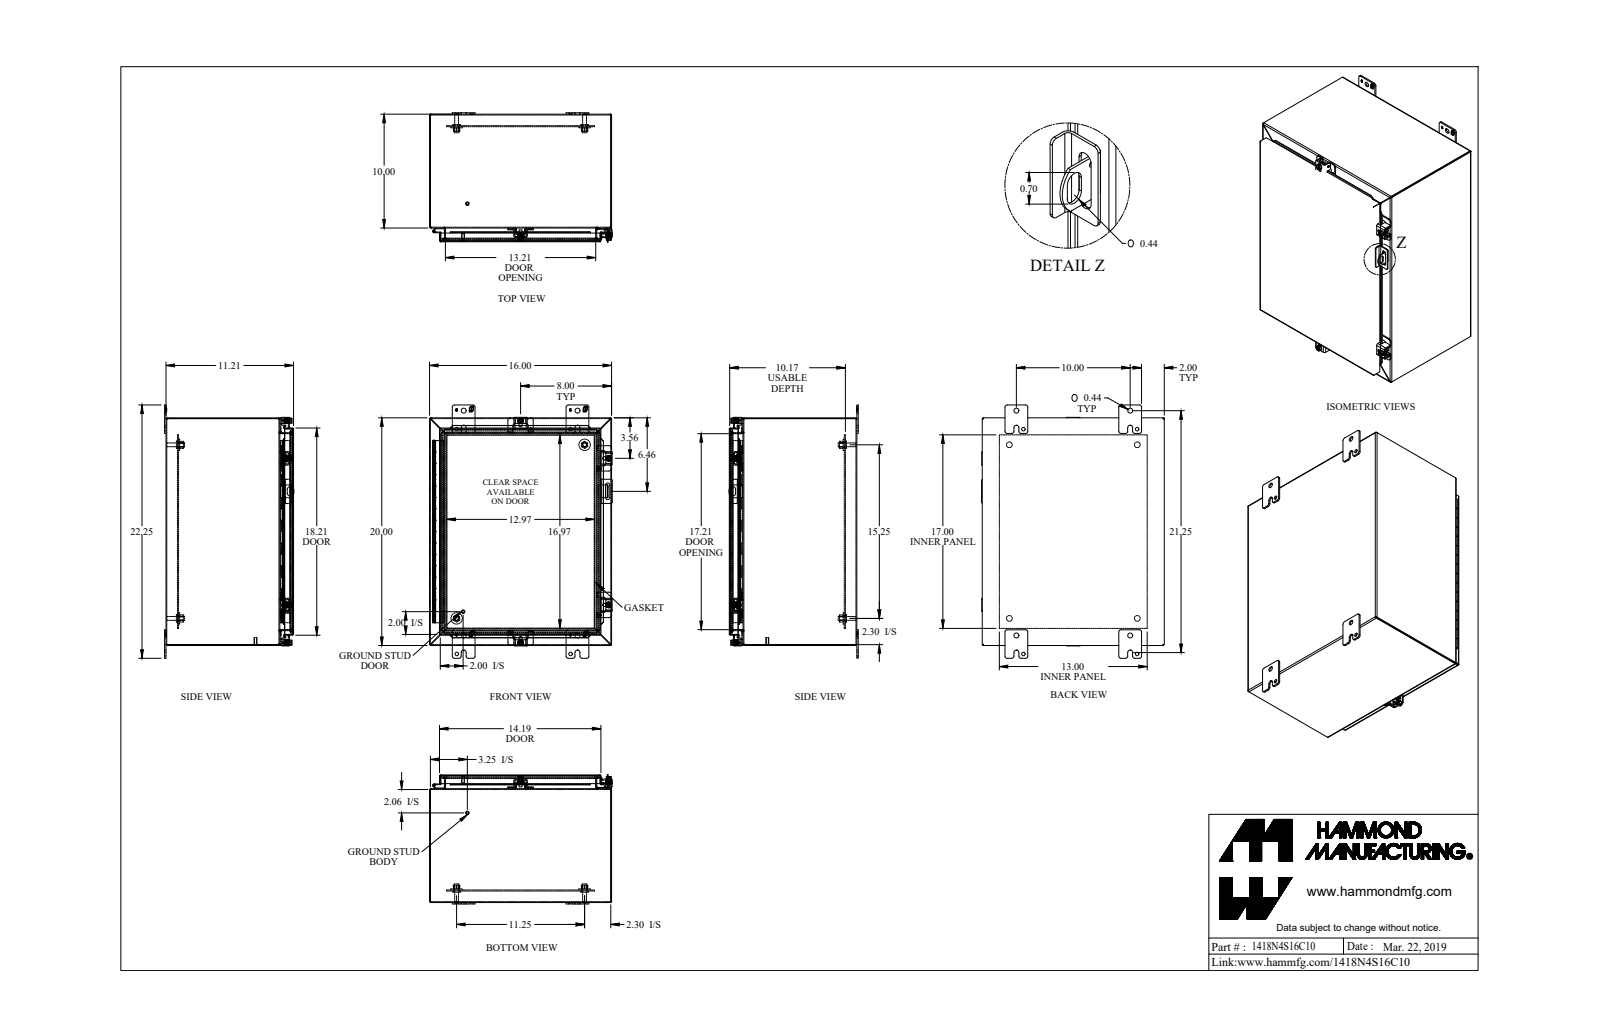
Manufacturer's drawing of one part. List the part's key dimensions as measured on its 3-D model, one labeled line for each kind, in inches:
Part name (STEP PRODUCT): 1418N4S16C10_Default
STEP written by: SolidWorks 2019 (CONFIG_CONTROL_DESIGN)
Units: inches
Bodies: 39 solids, 1329 faces (728 planar, 467 cylindrical, 134 other)
Overall size (bounding box): 22.25 × 16.063 × 11.375
Volume: 142.1 in³ · Surface area: 3 791 in²
Round holes (diameter × count): ⌀0.213 ×4, ⌀0.265 ×4, ⌀0.313 ×4, ⌀0.375 ×4, ⌀0.437 ×4, ⌀0.5 ×4, ⌀0.307 ×2, ⌀0.445 ×2, ⌀0.11 ×1, ⌀0.125 ×1
Round bosses / shafts (diameter × count): ⌀0.65 ×4, ⌀0.5 ×4, ⌀0.39 ×4, ⌀0.375 ×4, ⌀0.332 ×4, ⌀0.244 ×4, ⌀1 ×2, ⌀0.313 ×2
Partial cylindrical surfaces — rounded edges, fillets, slot ends (radius × count): R0.188 ×26, R0.036 ×24, R0.108 ×24, R0.048 ×21, R0.143 ×21, R0.25 ×20, R0.125 ×10, R0.045 ×8
Main face-to-face distances: 0.072, 15.928, 19.928, 0.072, 11.066, 11.138, 11.138, 0.937, 11.21, 1.009
Hole centre spacings: 18.263, 6.013, 10, 2.434, 3.065, 11.041, 11.25, 15.25
